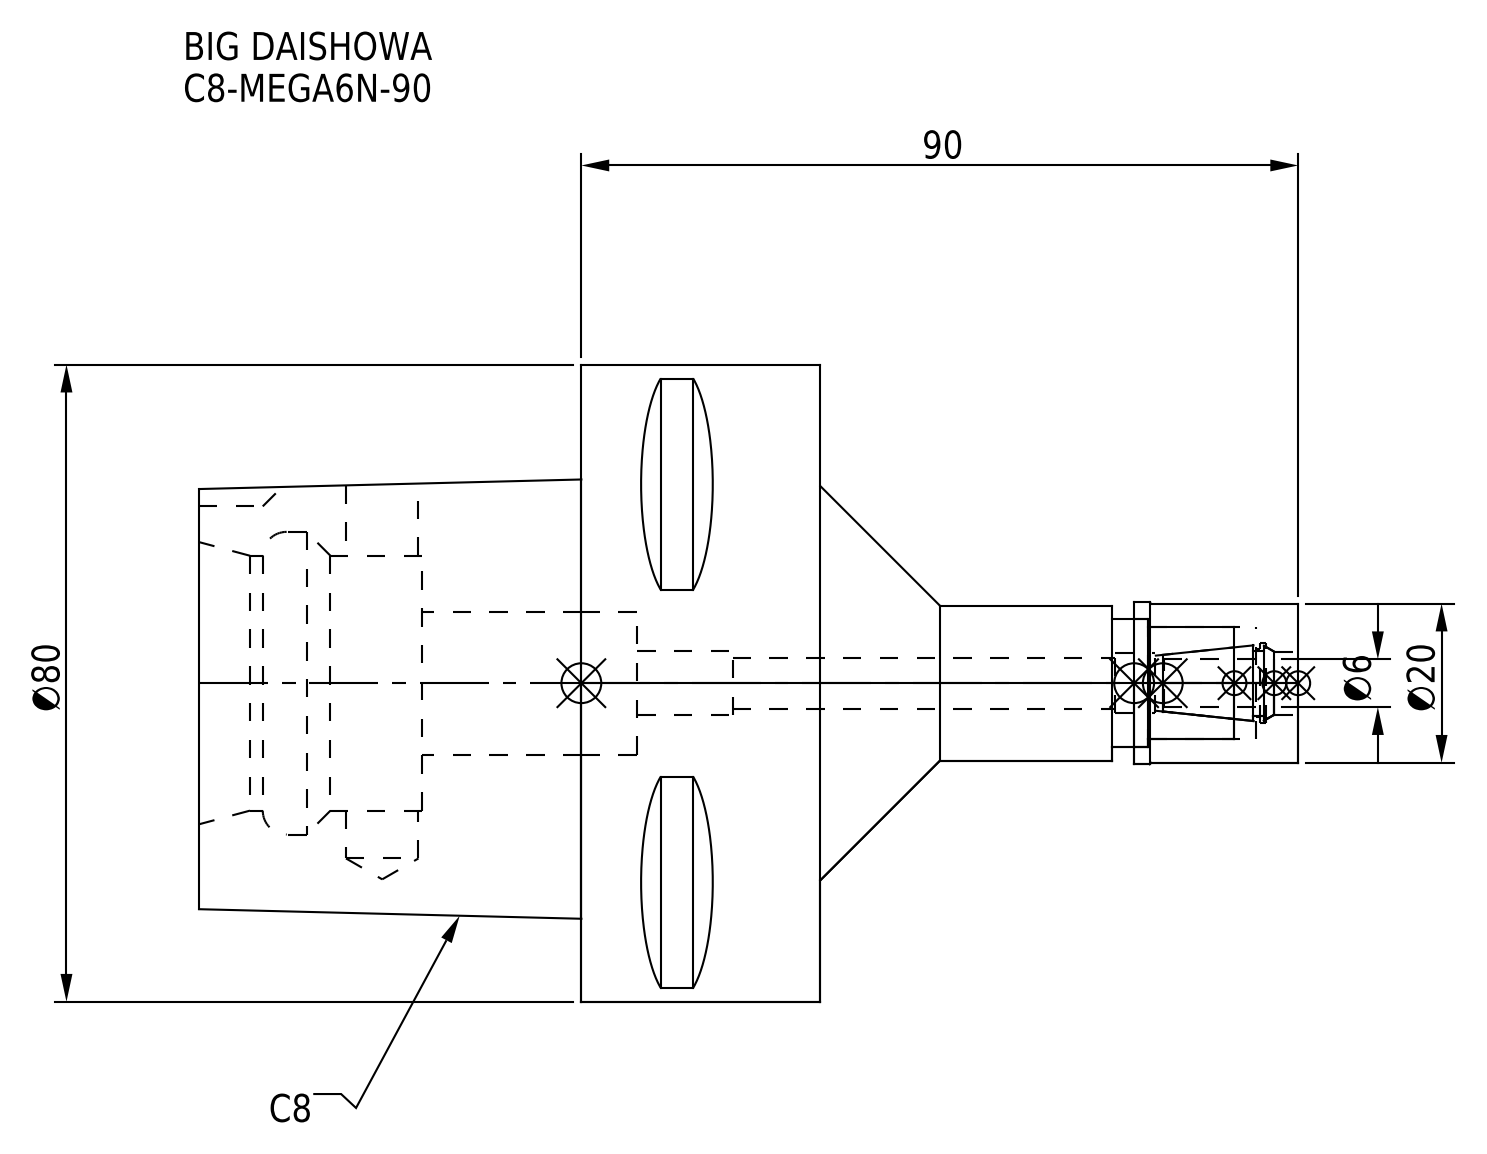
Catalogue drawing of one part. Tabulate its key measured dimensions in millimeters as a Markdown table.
| quantity | value |
| --- | --- |
| part name | MGN6_1.stp; C8-MEGA6N-90-060_ASM.stp; C8-MEGA6N-90; C8-MEGA6N-90-060-FreeParts (+3 more) |
| STEP written by | SolidWorks 2019 (CONFIG_CONTROL_DESIGN) |
| units | millimeters |
| bodies | 2 solids, 98 faces (39 planar, 41 cylindrical, 18 other) |
| overall size | 138 × 80 × 80 |
| volume | 247 999 mm³ |
| surface area | 37 990 mm² |
| round holes (diameter × count) | 6.4 × 1, 7.5 × 1, 7.9 × 1, 8 × 1, 8.5 × 1, 9.1 × 1, 10 × 1, 14 × 1, 16 × 1, 18 × 1, 32 × 1, 38 × 1 |
| round bosses / shafts (diameter × count) | 80 × 1, 20.3 × 1, 20 × 1, 19.5 × 1 |
| partial cylindrical surfaces (radius × count) | 6 × 1 |
| main face-to-face distances | 30, 48, 78, 20, 50, 28, 32.55, 70.68, 60, 90 |
